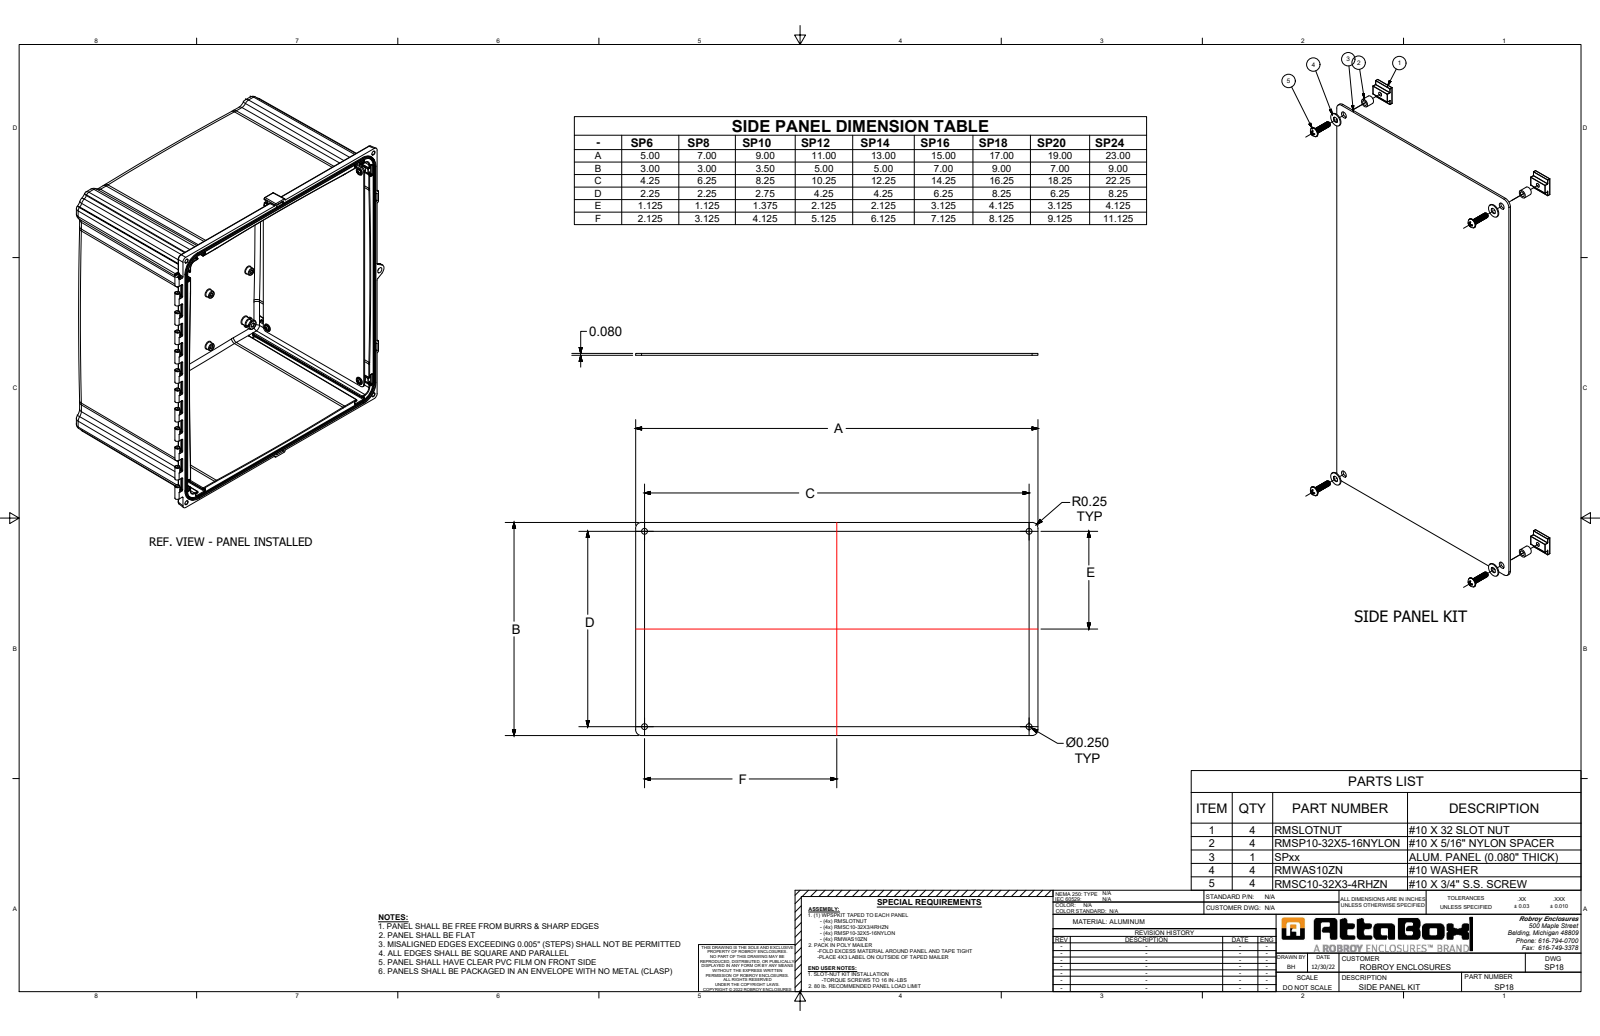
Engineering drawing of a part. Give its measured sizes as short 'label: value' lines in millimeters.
name: SP18_Default
written by: SolidWorks 2023 (CONFIG_CONTROL_DESIGN)
unit: mm
bodies: 1 solid, 14 faces (6 planar, 8 cylindrical, 0 other)
size: 431.8 × 228.6 × 2
volume: 200 200 mm³; area: 199 900 mm²
holes: 4× ⌀6.4
rounds: 4× R6.4
face distances: 2, 228.6, 431.8
hole spacings: 209.6, 412.8, 462.9
